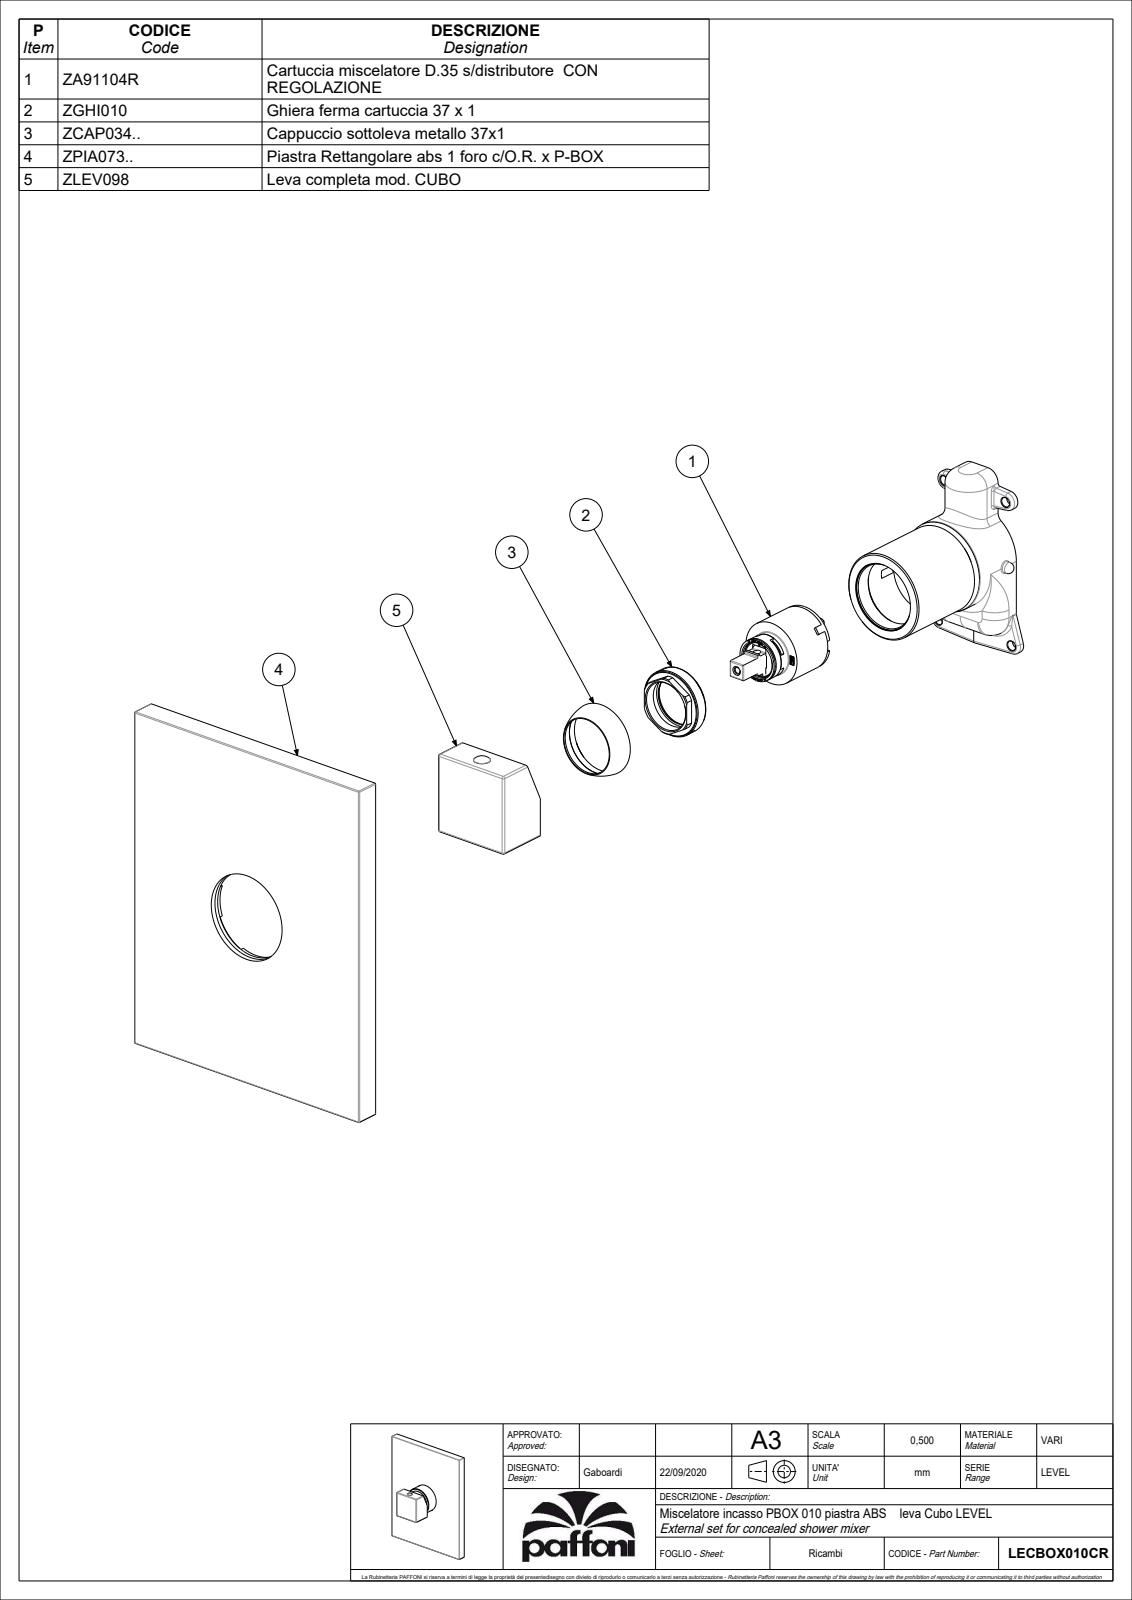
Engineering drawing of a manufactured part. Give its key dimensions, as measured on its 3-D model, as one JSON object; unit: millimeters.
{"part_name": "LECBOX010CR", "step_written_by": "CREO PARAMETRIC BY PTC INC, 2020044 (CONFIG_CONTROL_DESIGN)", "units": "millimeters", "bodies": {"solids": 2, "faces": 1015, "planar": 623, "cylindrical": 249, "other": 143}, "overall_size": [192, 154, 65.6], "volume_mm3": 302202, "surface_area_mm2": 118539, "round_holes": [[5, 3], [7, 3], [2, 2], [4, 2], [3.3, 1], [6, 1], [11, 1], [19.5, 1], [19.9, 1], [26.8, 1], [29, 1], [31, 1]], "round_bosses_or_shafts": [[4.8, 2], [57, 1], [48.1, 1], [39, 1], [35, 1], [34.8, 1], [32.2, 1], [23.5, 1]], "partial_cylinders_radius": [[0.5, 35], [0.15, 11], [1, 10], [0.3, 4], [2.5, 1], [3.95, 1], [7, 1], [9.3, 1]], "face_to_face_distances": [13.5, 3, 10.5, 23.5, 130.5, 52.1, 31, 154, 99.5, 76], "hole_center_spacings": [8.6, 13.45, 15.13, 21.93, 14, 14.1, 18]}
